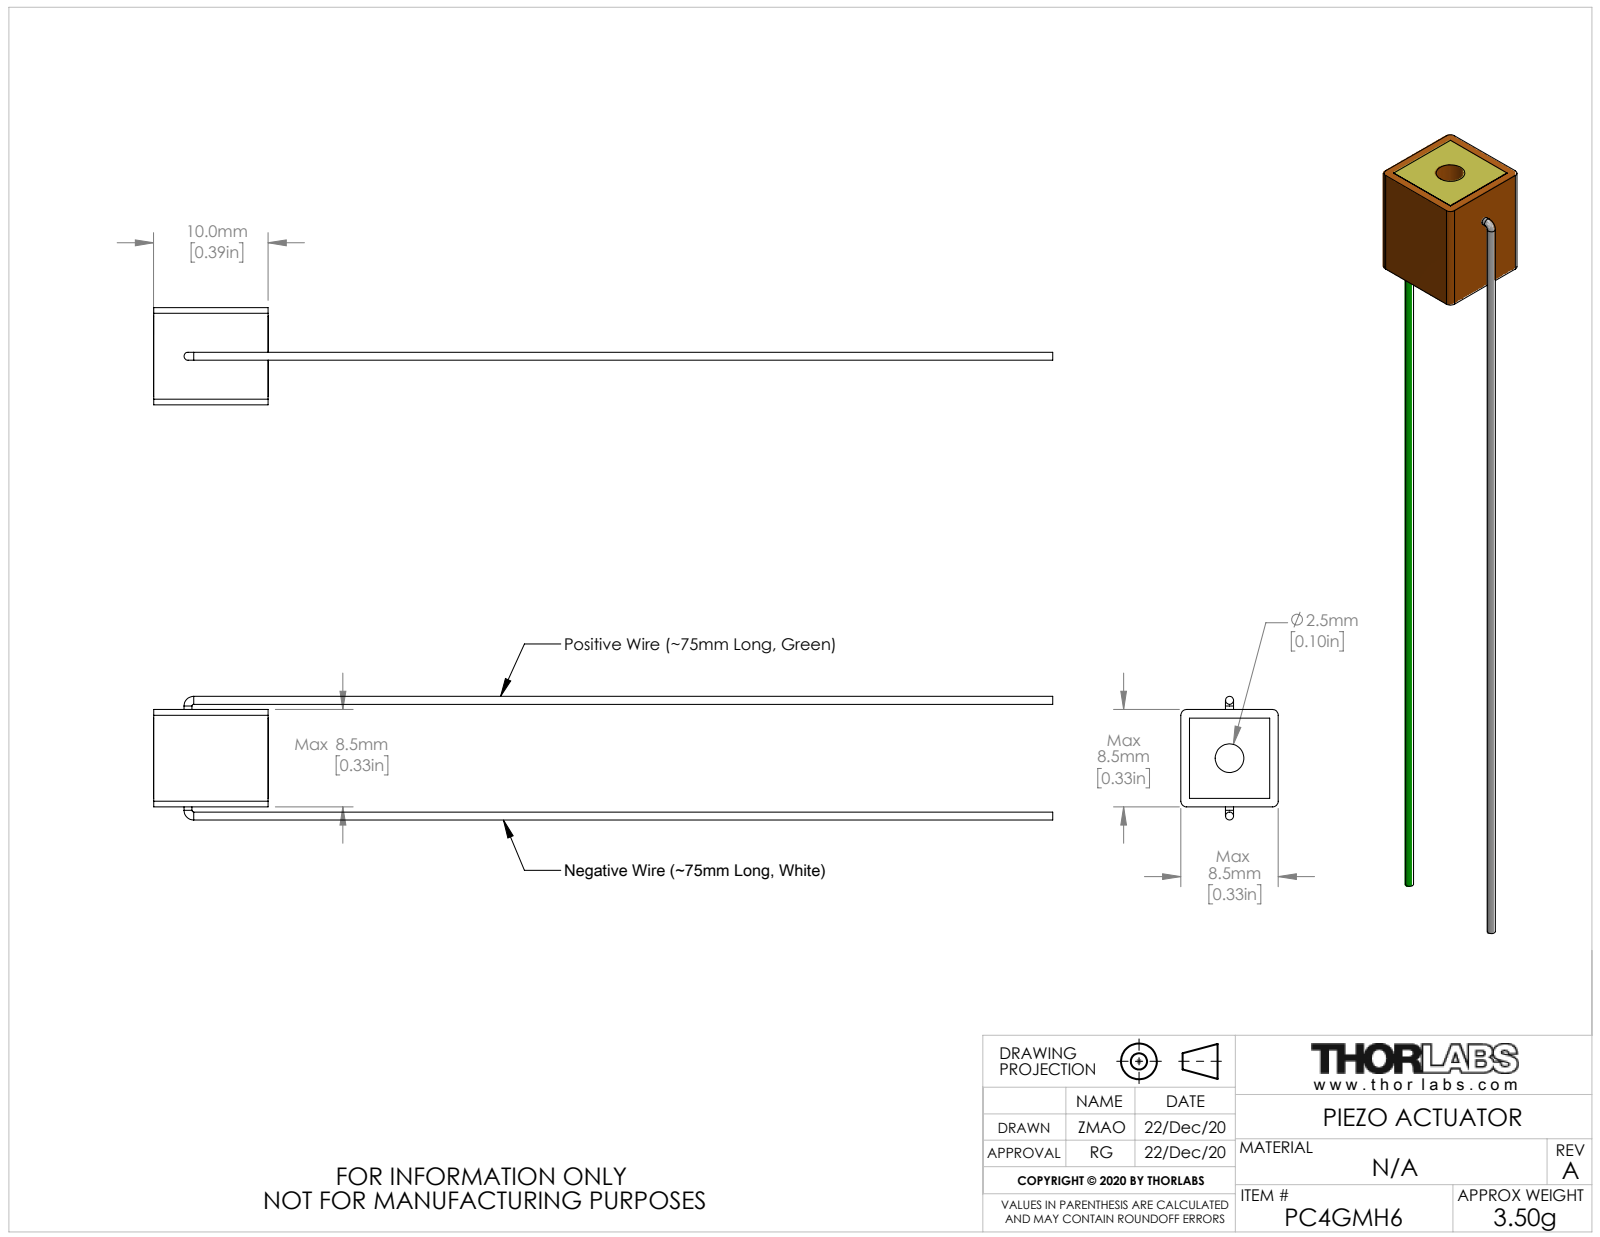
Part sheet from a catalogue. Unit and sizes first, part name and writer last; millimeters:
Units: millimetres
Overall size (bounding box): 78.51 × 10.8 × 8.5
Round holes (diameter × count): ⌀2.5 ×1
Round bosses / shafts (diameter × count): ⌀0.7 ×3
Partial cylindrical surfaces — rounded edges, fillets, slot ends (radius × count): R0.5 ×4
Main face-to-face distances: 8.5, 10.01, 10.02, 10, 68.49, 68.5, 78.5, 78.51, 0.75, 7.75
Volume: 731 mm³ · Surface area: 880 mm²
Bodies: 1 solid, 36 faces (18 planar, 14 cylindrical, 4 other)
Part name (STEP PRODUCT): CTN017066-E0W
STEP written by: SolidWorks 2018 (AUTOMOTIVE_DESIGN)
